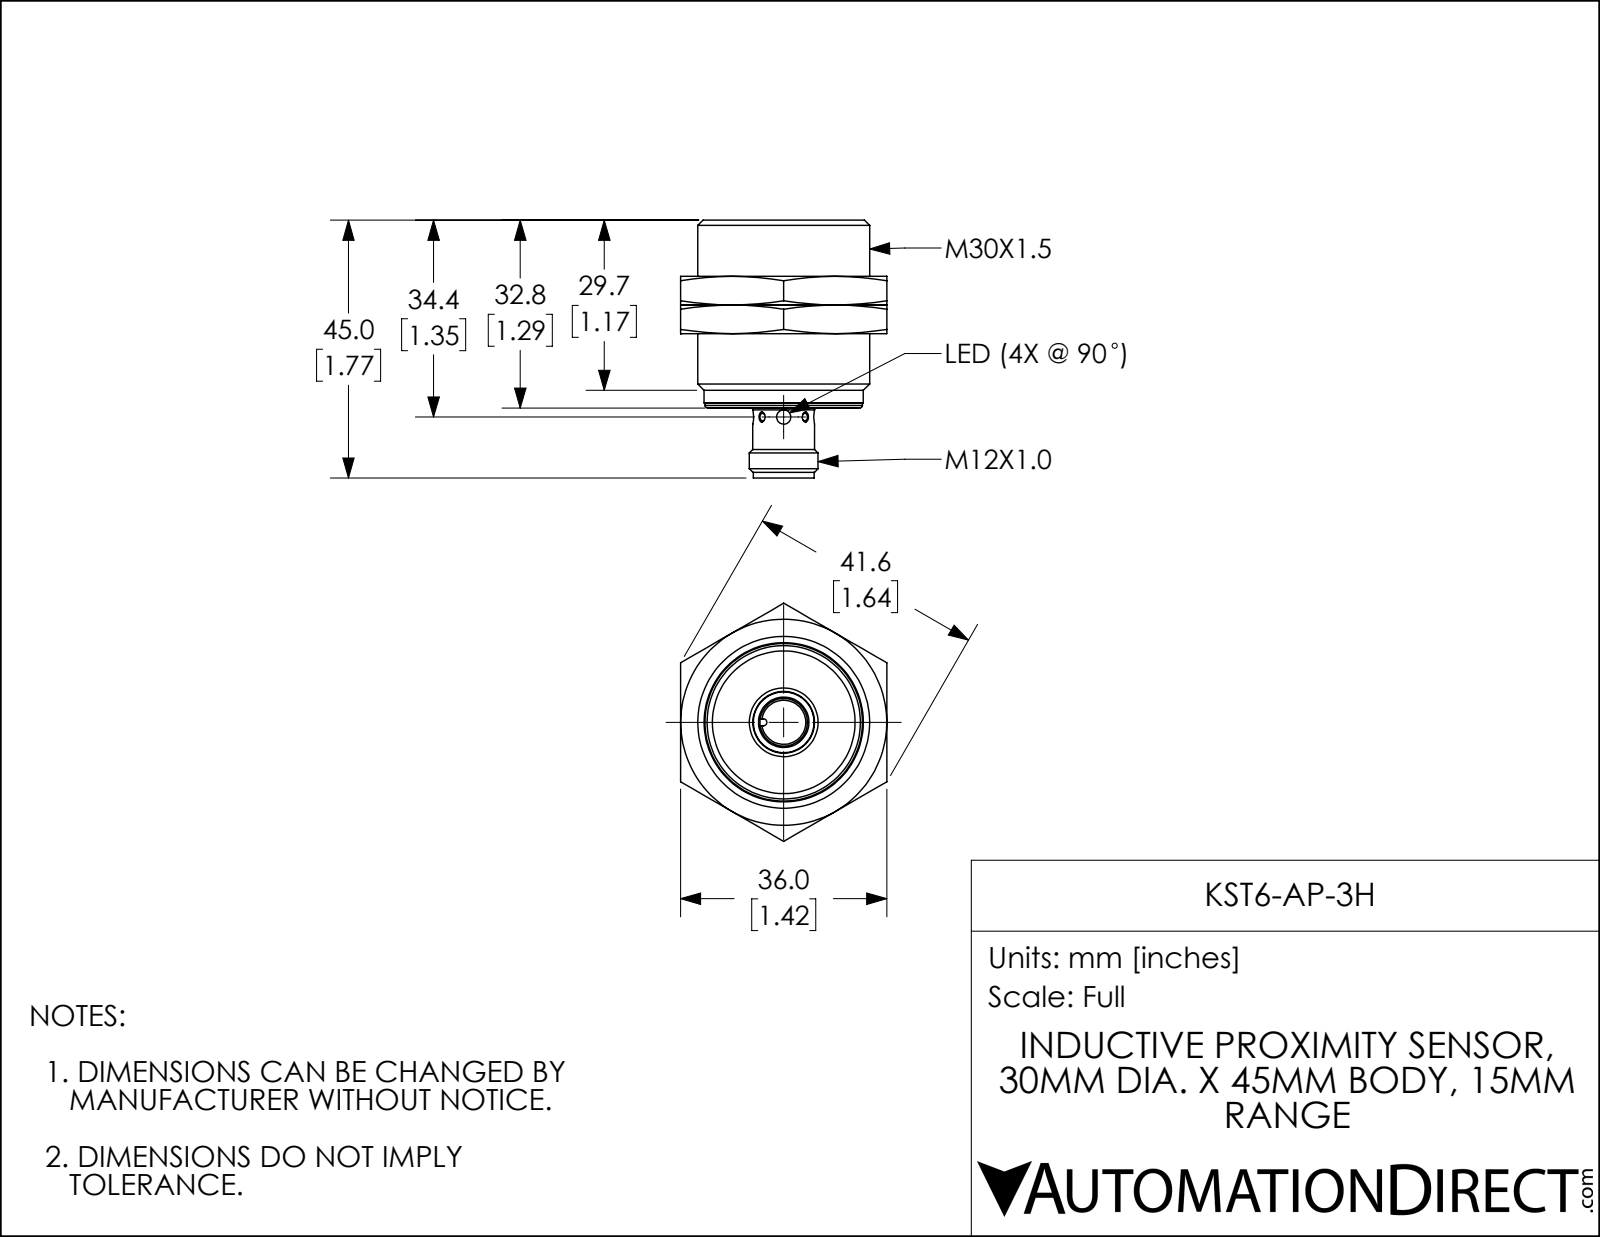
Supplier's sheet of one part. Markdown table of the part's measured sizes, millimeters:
| quantity | value |
| --- | --- |
| part name | KST6-AP-3H |
| STEP written by | SolidWorks 2017 (AUTOMOTIVE_DESIGN) |
| units | millimeters |
| bodies | 3 solids, 73 faces (26 planar, 20 cylindrical, 27 other) |
| overall size | 45 × 41.6 × 36 |
| volume | 28 190 mm³ |
| surface area | 9 045 mm² |
| round holes (diameter × count) | 2.5 × 2, 8.3 × 1, 27.3 × 1, 28.4 × 1 |
| round bosses / shafts (diameter × count) | 30 × 1, 27.8 × 1, 27.5 × 1, 27.3 × 1, 12 × 1, 10.8 × 1, 10.6 × 1 |
| partial cylindrical surfaces (radius × count) | 0.6 × 1, 4.7 × 1 |
| main face-to-face distances | 5, 14.8, 36, 18, 32.8, 23, 9.8, 13, 10, 19.8 |
